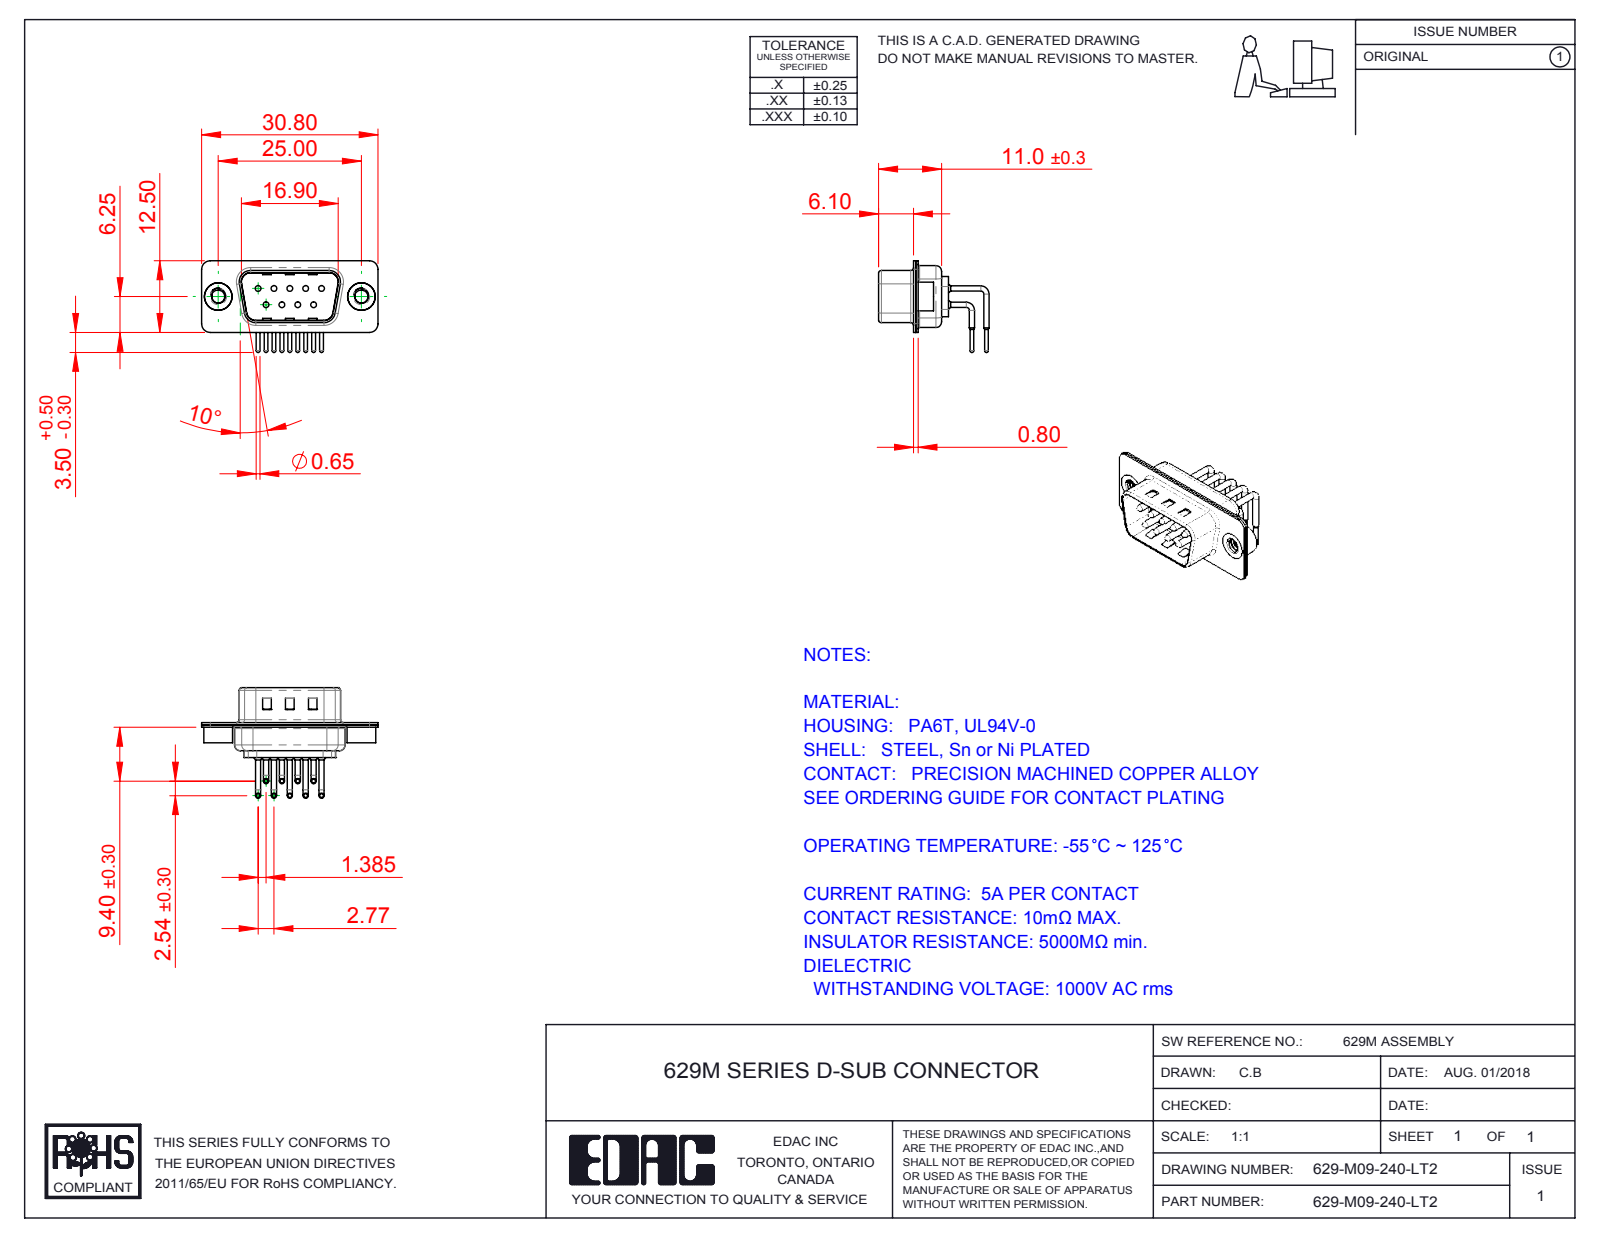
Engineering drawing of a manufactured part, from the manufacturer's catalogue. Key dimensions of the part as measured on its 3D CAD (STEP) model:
Part name (STEP PRODUCT): 629M Contact Row 1; 629M Shell Rear_09 Contacts; 629M Shell Front_09 Contacts; 629M Housing_09 Contacts (+3 more)
STEP written by: SolidWorks 2016 (CONFIG_CONTROL_DESIGN)
Units: millimetres
Bodies: 14 solids, 1294 faces (683 planar, 453 cylindrical, 158 other)
Overall size (bounding box): 30.8 × 19.29 × 16
Volume: 1 381 mm³ · Surface area: 3 912 mm²
Round holes (diameter × count): ⌀1 ×9, ⌀1.7 ×9, ⌀2 ×9, ⌀2.26 ×2, ⌀4 ×2, ⌀4.8 ×2
Round bosses / shafts (diameter × count): ⌀0.9 ×18, ⌀1.5 ×9, ⌀0.65 ×9, ⌀5 ×2, ⌀4.9 ×2
Partial cylindrical surfaces — rounded edges, fillets, slot ends (radius × count): R1.5 ×16, R2 ×12, R1.01 ×9, R0.5 ×8, R1.6 ×8, R0.25 ×4, R0.6 ×4, R0.65 ×4
Main face-to-face distances: 0.4, 0.85, 0.8, 9.55, 1.25, 10.4, 8.7, 0.35, 6.1, 5.7
Hole centre spacings: 3.16, 2.77, 5.54, 5.03, 5.04, 8.31, 7.1, 7.48
